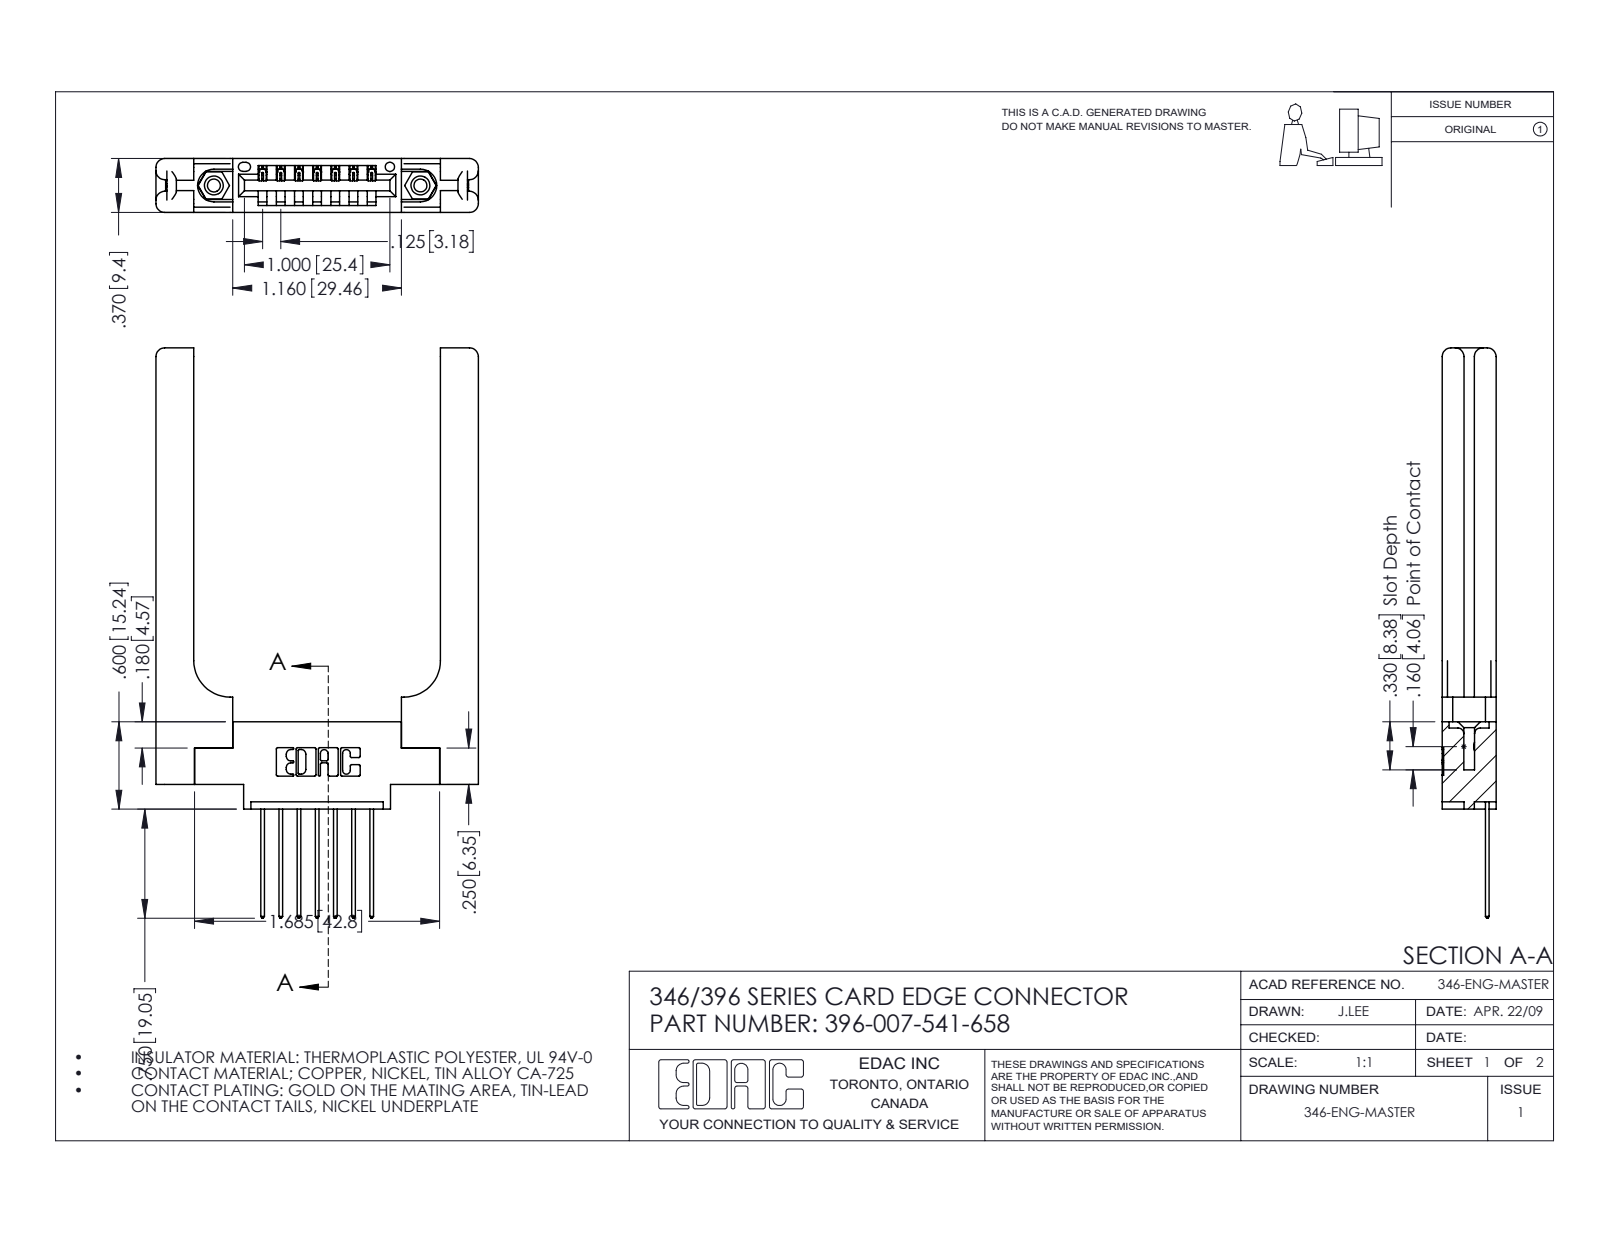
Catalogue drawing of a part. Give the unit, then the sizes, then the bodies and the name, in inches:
Units: inches
Overall size (bounding box): 3.92 × 2.216 × 0.37
Round holes (diameter × count): ⌀0.089 ×2, ⌀0.125 ×2, ⌀0.156 ×2, ⌀0.064 ×1
Round bosses / shafts (diameter × count): ⌀0.155 ×2
Partial cylindrical surfaces — rounded edges, fillets, slot ends (radius × count): R0.01 ×22, R0.06 ×16, R0.006 ×14, R0.01 ×14, R0.007 ×6, R0.031 ×6, R0.026 ×3, R0.03 ×2
Main face-to-face distances: 0.37, 0.15, 0.22, 0.072, 0.148, 0.25, 0.102, 0.048, 0.322, 0.173
Hole centre spacings: 0.246, 1.217, 1.42
Volume: 0.765 in³ · Surface area: 17.61 in²
Bodies: 12 solids, 788 faces (508 planar, 220 cylindrical, 60 other)
Part name (STEP PRODUCT): 346-220-058_345-220-058; 396-007-541-658; 345-250-001_345-250-001-102; 346 Part_0.170 Offset - 0.156 Dia-TH (+1 more)
STEP written by: SolidWorks 2016 (CONFIG_CONTROL_DESIGN)
